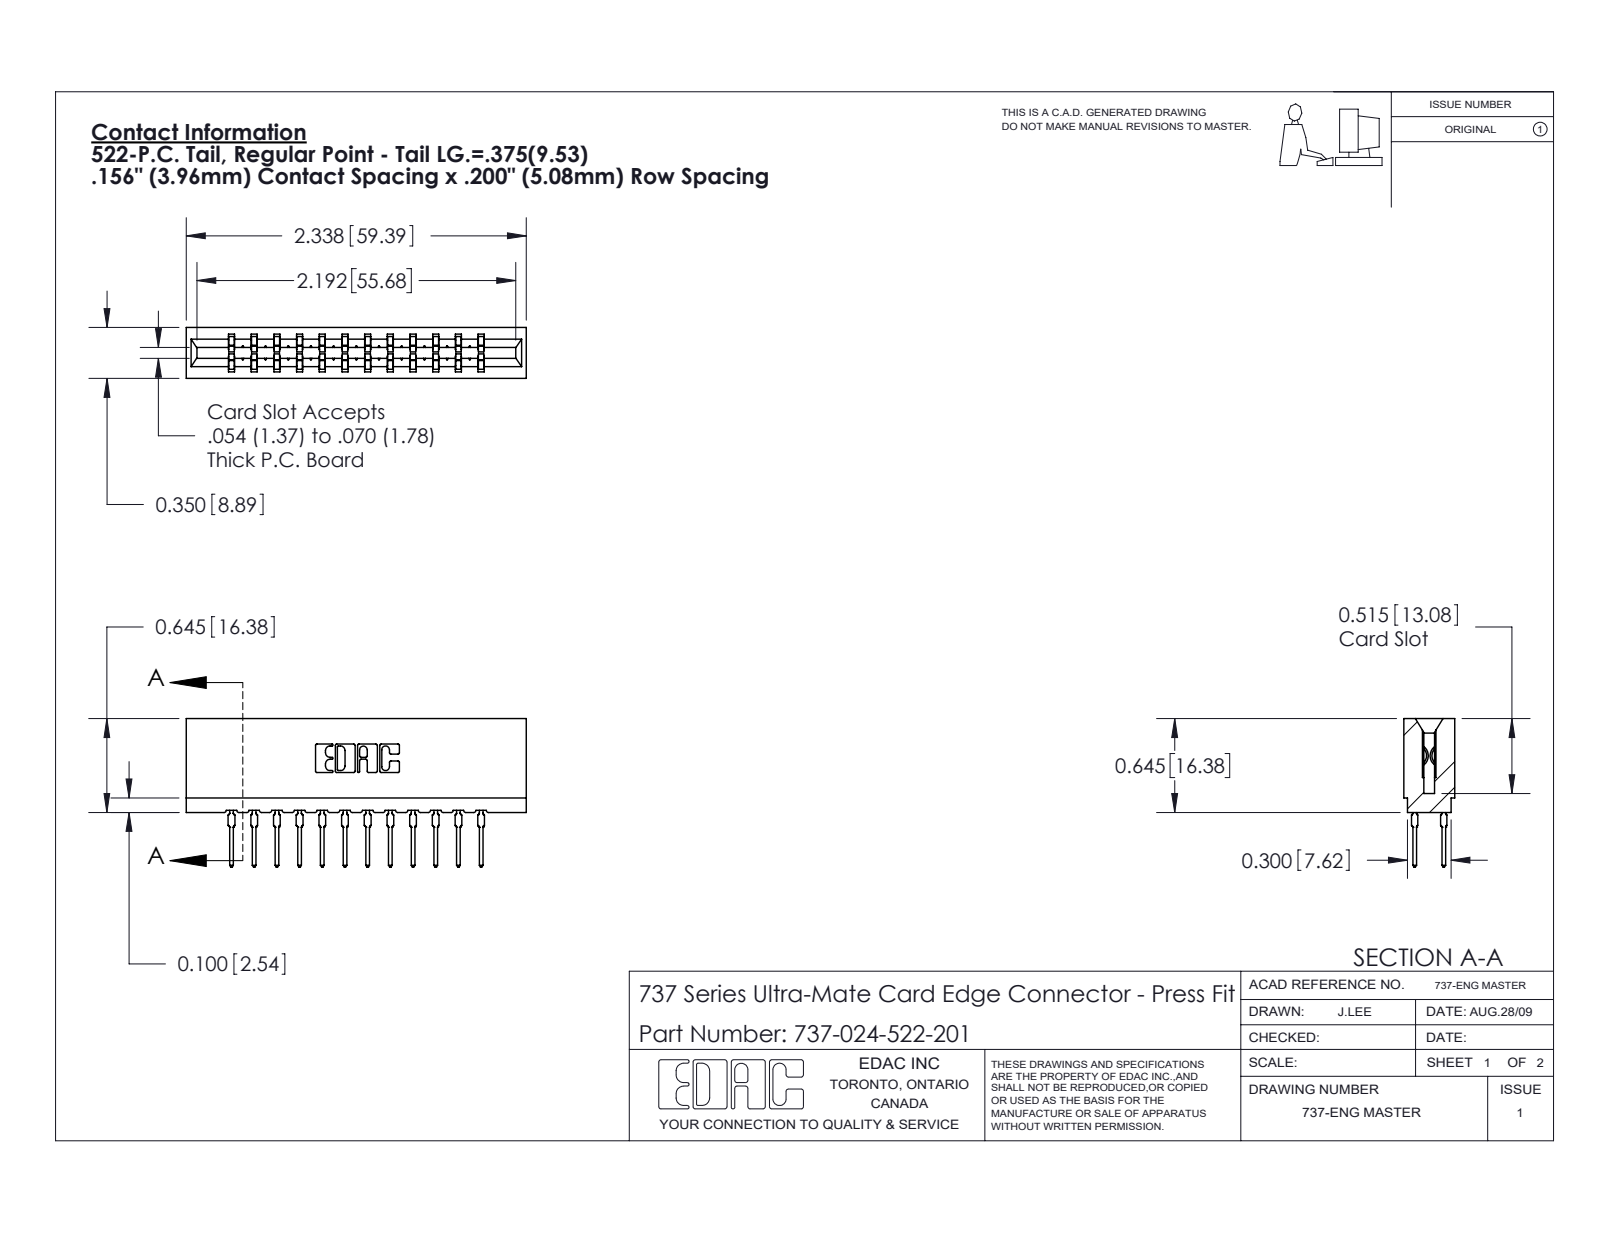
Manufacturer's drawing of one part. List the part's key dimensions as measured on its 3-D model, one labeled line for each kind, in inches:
Part name (STEP PRODUCT): 737 Part_Insulator Option - 01; 737-024-522-201; 745-292-001_522
STEP written by: SolidWorks 2020 (CONFIG_CONTROL_DESIGN)
Units: inches
Bodies: 25 solids, 2254 faces (1170 planar, 460 cylindrical, 624 other)
Overall size (bounding box): 2.338 × 1.021 × 0.35
Volume: 0.371 in³ · Surface area: 12.82 in²
Partial cylindrical surfaces — rounded edges, fillets, slot ends (radius × count): R0.021 ×48, R0.015 ×24, R0.01 ×22, R0.005 ×8, R0.011 ×8, R0.007 ×6, R0.031 ×6, R0.026 ×3
Main face-to-face distances: 0.138, 0.212, 0.156, 0.35, 0.624, 0.312, 0.78, 0.468, 0.074, 0.354
